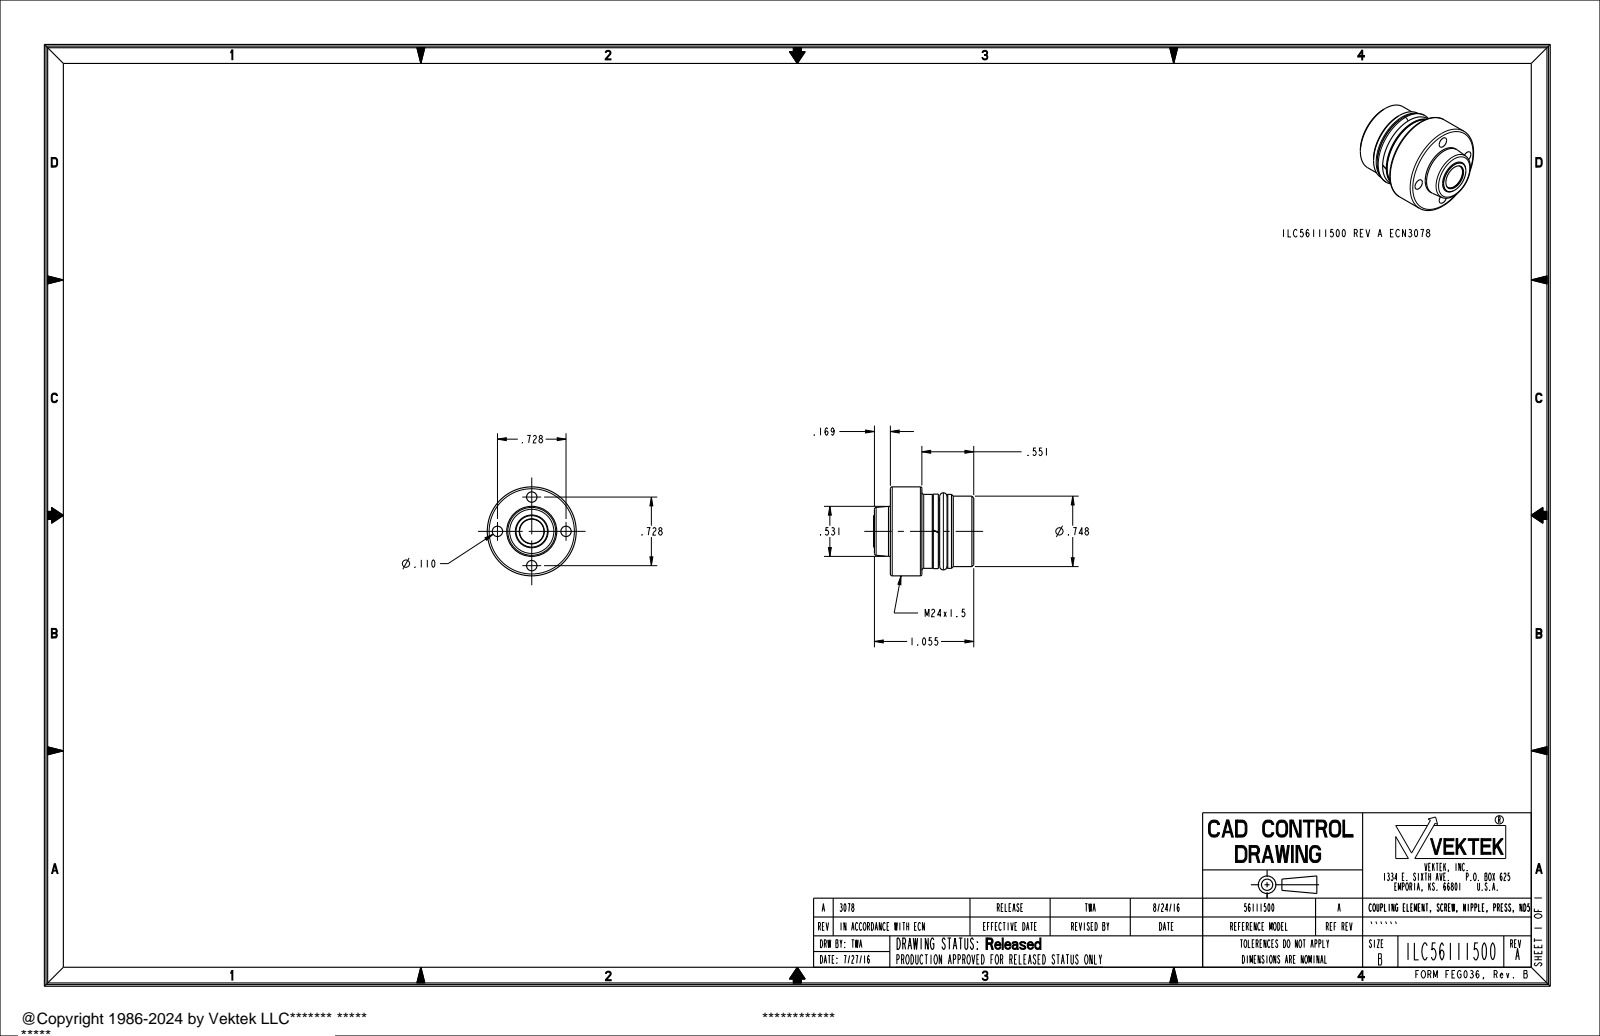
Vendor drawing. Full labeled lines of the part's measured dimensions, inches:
Part name (STEP PRODUCT): ILC56111500
STEP written by: PRO/ENGINEER BY PARAMETRIC TECHNOLOGY CORPORATION, 2013320 (CONFIG_CONTROL_DESIGN)
Units: inches
Bodies: 2 solids, 80 faces (14 planar, 28 cylindrical, 38 other)
Overall size (bounding box): 1.063 × 0.945 × 0.945
Volume: 0.519 in³ · Surface area: 5.178 in²
Round holes (diameter × count): ⌀0.11 ×4, ⌀0.26 ×1
Round bosses / shafts (diameter × count): ⌀0.945 ×1, ⌀0.791 ×1, ⌀0.785 ×1, ⌀0.748 ×1, ⌀0.661 ×1, ⌀0.531 ×1, ⌀0.335 ×1
Main face-to-face distances: 0.886, 0.51, 0.376, 0.455, 0.055, 0.431, 0.335, 0.12, 0.175, 0.551
Hole centre spacings: 0.364, 0.515, 0.728
